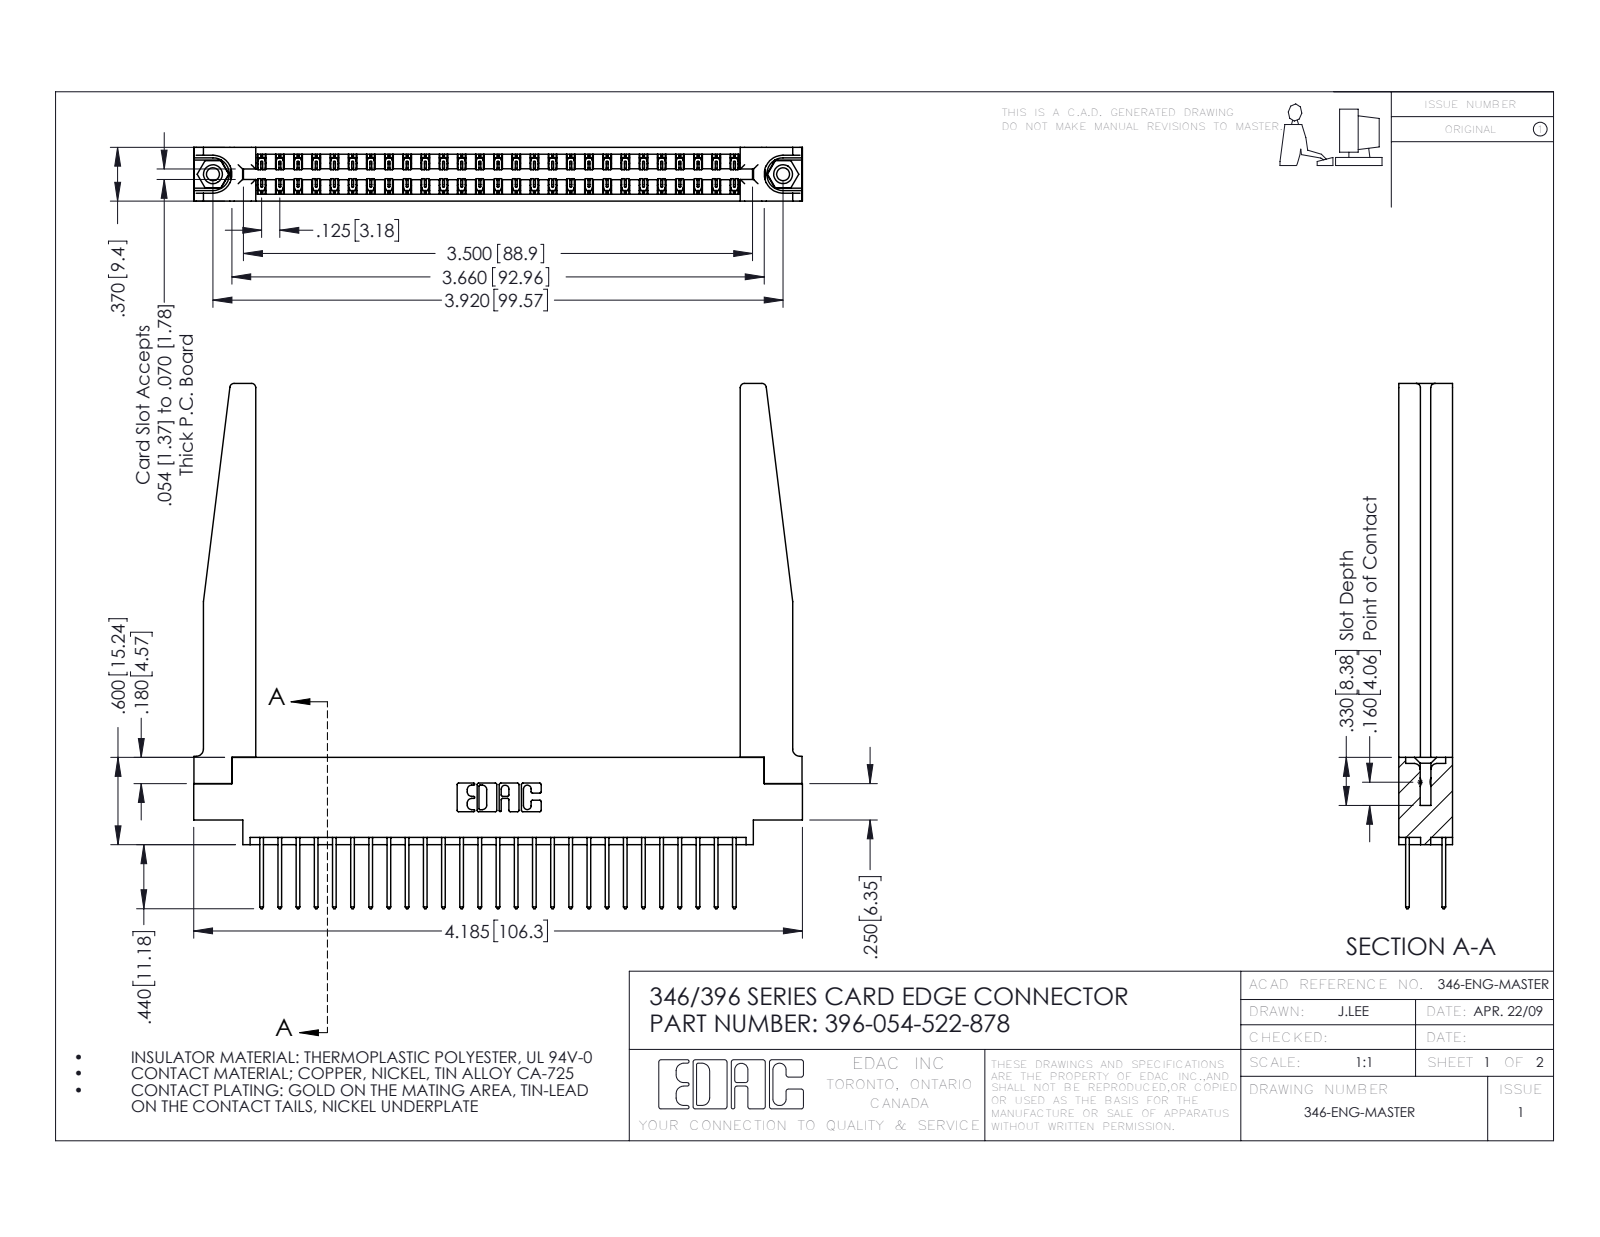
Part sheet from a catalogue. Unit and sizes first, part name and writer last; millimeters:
Units: millimetres
Overall size (bounding box): 106.3 × 91.7 × 9.4
Round holes (diameter × count): ⌀2.3 ×2, ⌀3.2 ×2, ⌀4 ×2, ⌀1.6 ×1
Round bosses / shafts (diameter × count): ⌀3.9 ×2
Partial cylindrical surfaces — rounded edges, fillets, slot ends (radius × count): R0.2 ×81, R0.3 ×54, R0.3 ×22, R0.8 ×8, R0.2 ×6, R0.8 ×6, R0.7 ×3, R0.4 ×2
Main face-to-face distances: 9.4, 1.2, 8.2, 1.8, 6.4, 3.8, 3.8, 7.6, 0.6, 7
Hole centre spacings: 6.2, 94.3, 99.6
Volume: 17 140 mm³ · Surface area: 21 190 mm²
Bodies: 59 solids, 3168 faces (2112 planar, 1004 cylindrical, 52 other)
Part name (STEP PRODUCT): 396-054-522-878; 345-292-001_345-293-122; 346-220-078_345-220-078; 345-250-001_345-250-001-102 (+1 more)
STEP written by: SolidWorks 2016 (CONFIG_CONTROL_DESIGN)
